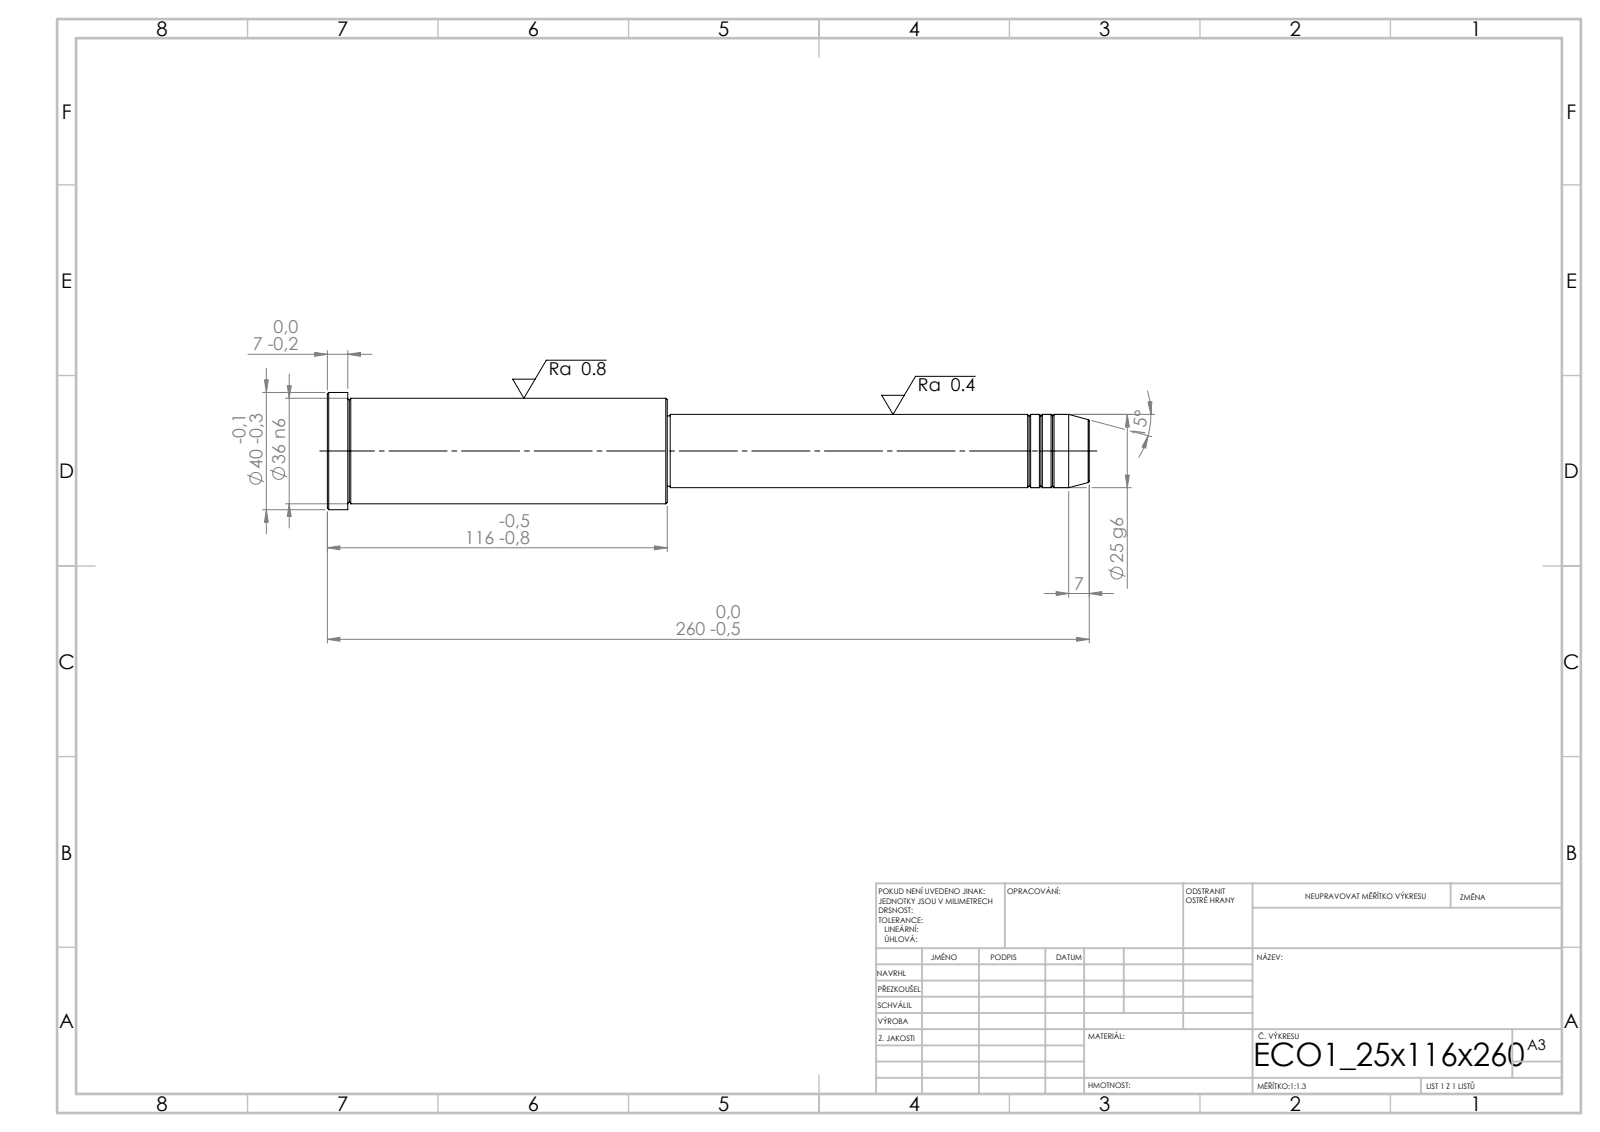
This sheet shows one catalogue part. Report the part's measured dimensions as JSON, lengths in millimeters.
{"step_written_by": "SolidWorks 2019 (CONFIG_CONTROL_DESIGN)", "units": "millimeters", "bodies": {"solids": 1, "faces": 43, "planar": 5, "cylindrical": 14, "other": 24}, "overall_size": [260, 40, 40], "volume_mm3": 189736, "surface_area_mm2": 27053, "round_bosses_or_shafts": [[40, 1], [36, 1], [25, 1], [24, 1]], "face_to_face_distances": [116, 144, 260, 253, 109, 7, 143, 1, 110, 117]}
